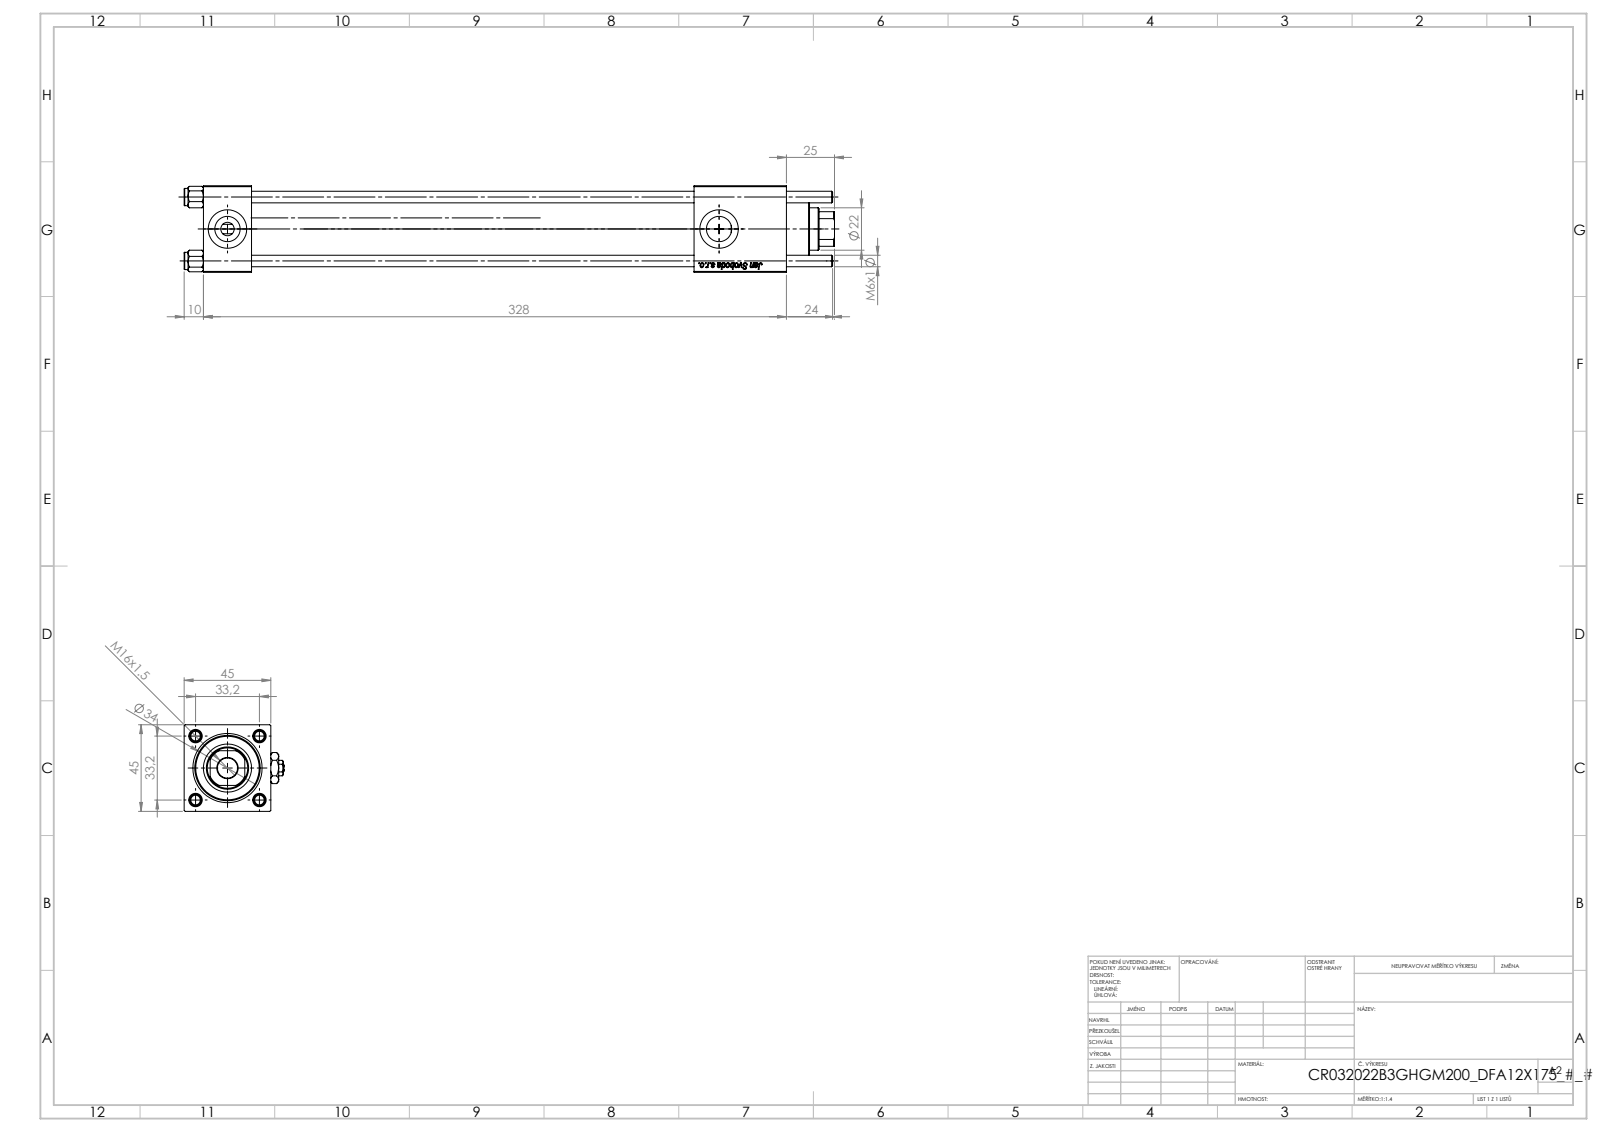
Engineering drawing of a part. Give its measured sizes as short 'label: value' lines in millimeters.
name: V215CR_B_TYCINKA; FEMALE_PART_FOR_DFA; V215_VC_A; V215CR_VCP_B (+3 more)
written by: SolidWorks 2019 (CONFIG_CONTROL_DESIGN)
unit: mm
bodies: 14 solids, 1289 faces (490 planar, 97 cylindrical, 702 other)
size: 338 × 52 × 45
volume: 370 750 mm³; area: 148 650 mm²
holes: 4× ⌀6, 2× ⌀7, 2× ⌀13.16, 2× ⌀20, 1× ⌀10.5, 1× ⌀22, 1× ⌀24, 1× ⌀25, 1× ⌀32, 1× ⌀33
bosses: 4× ⌀9, 1× ⌀38, 1× ⌀34, 1× ⌀28, 1× ⌀12, 1× ⌀10
rounds: 1× R9.75, 1× R10.5
face distances: 45, 25, 303, 255, 230, 44.8, 278, 48, 274.3, 249.3
hole spacings: 23.48, 33.2, 46.95, 255.5
